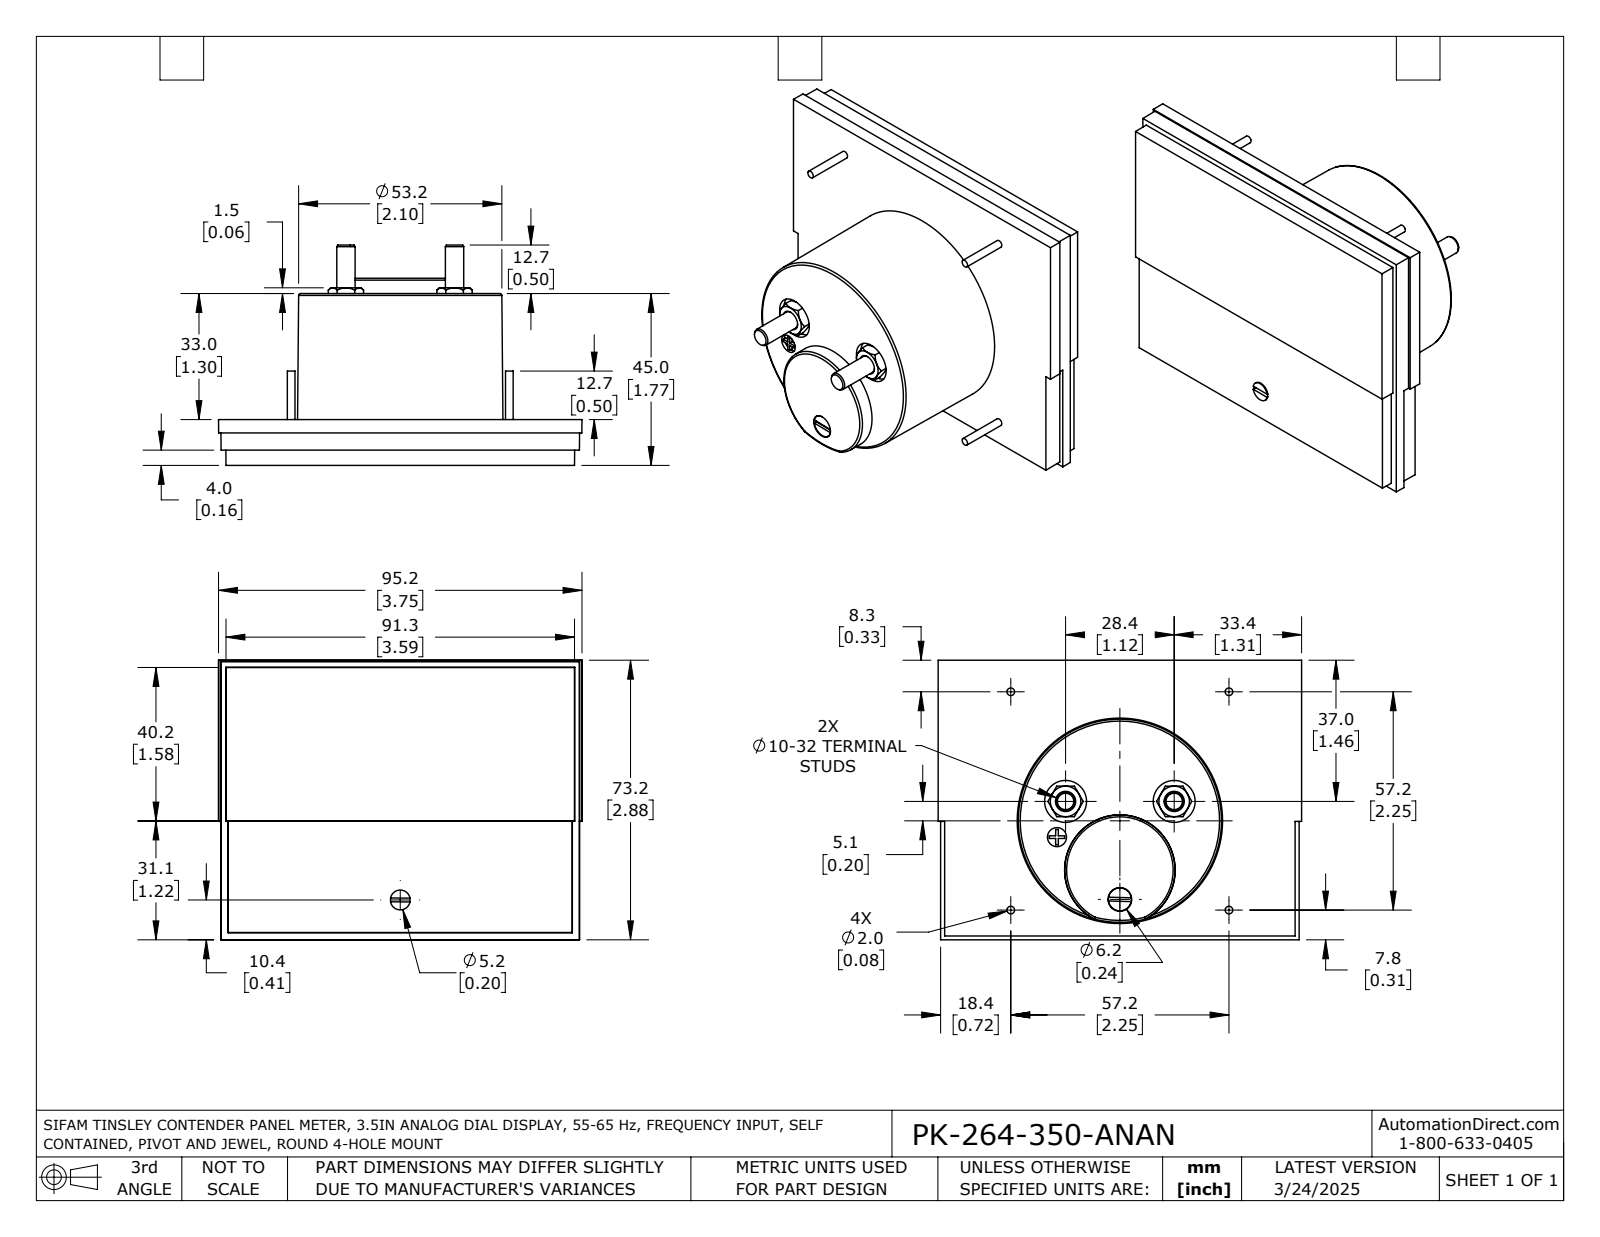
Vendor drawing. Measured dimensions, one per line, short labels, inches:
name: PK-264-350-ANAN
written by: SolidWorks 2021 (AUTOMOTIVE_DESIGN)
unit: in
bodies: 1 solid, 163 faces (76 planar, 31 cylindrical, 56 other)
size: 3.748 × 2.882 × 2.272
volume: 9.446 in³; area: 38.39 in²
holes: 2× ⌀0.433, 1× ⌀0.197, 1× ⌀0.244
bosses: 4× ⌀0.079, 2× ⌀0.189, 1× ⌀0.236, 1× ⌀0.205
rounds: 1× R0.1
face distances: 0.472, 0.03, 0.443, 1.772, 1.299, 1.742, 0.157, 0.073, 0.315, 1.457
hole spacings: 1.155, 0.379, 0.912, 1.12, 1.263
